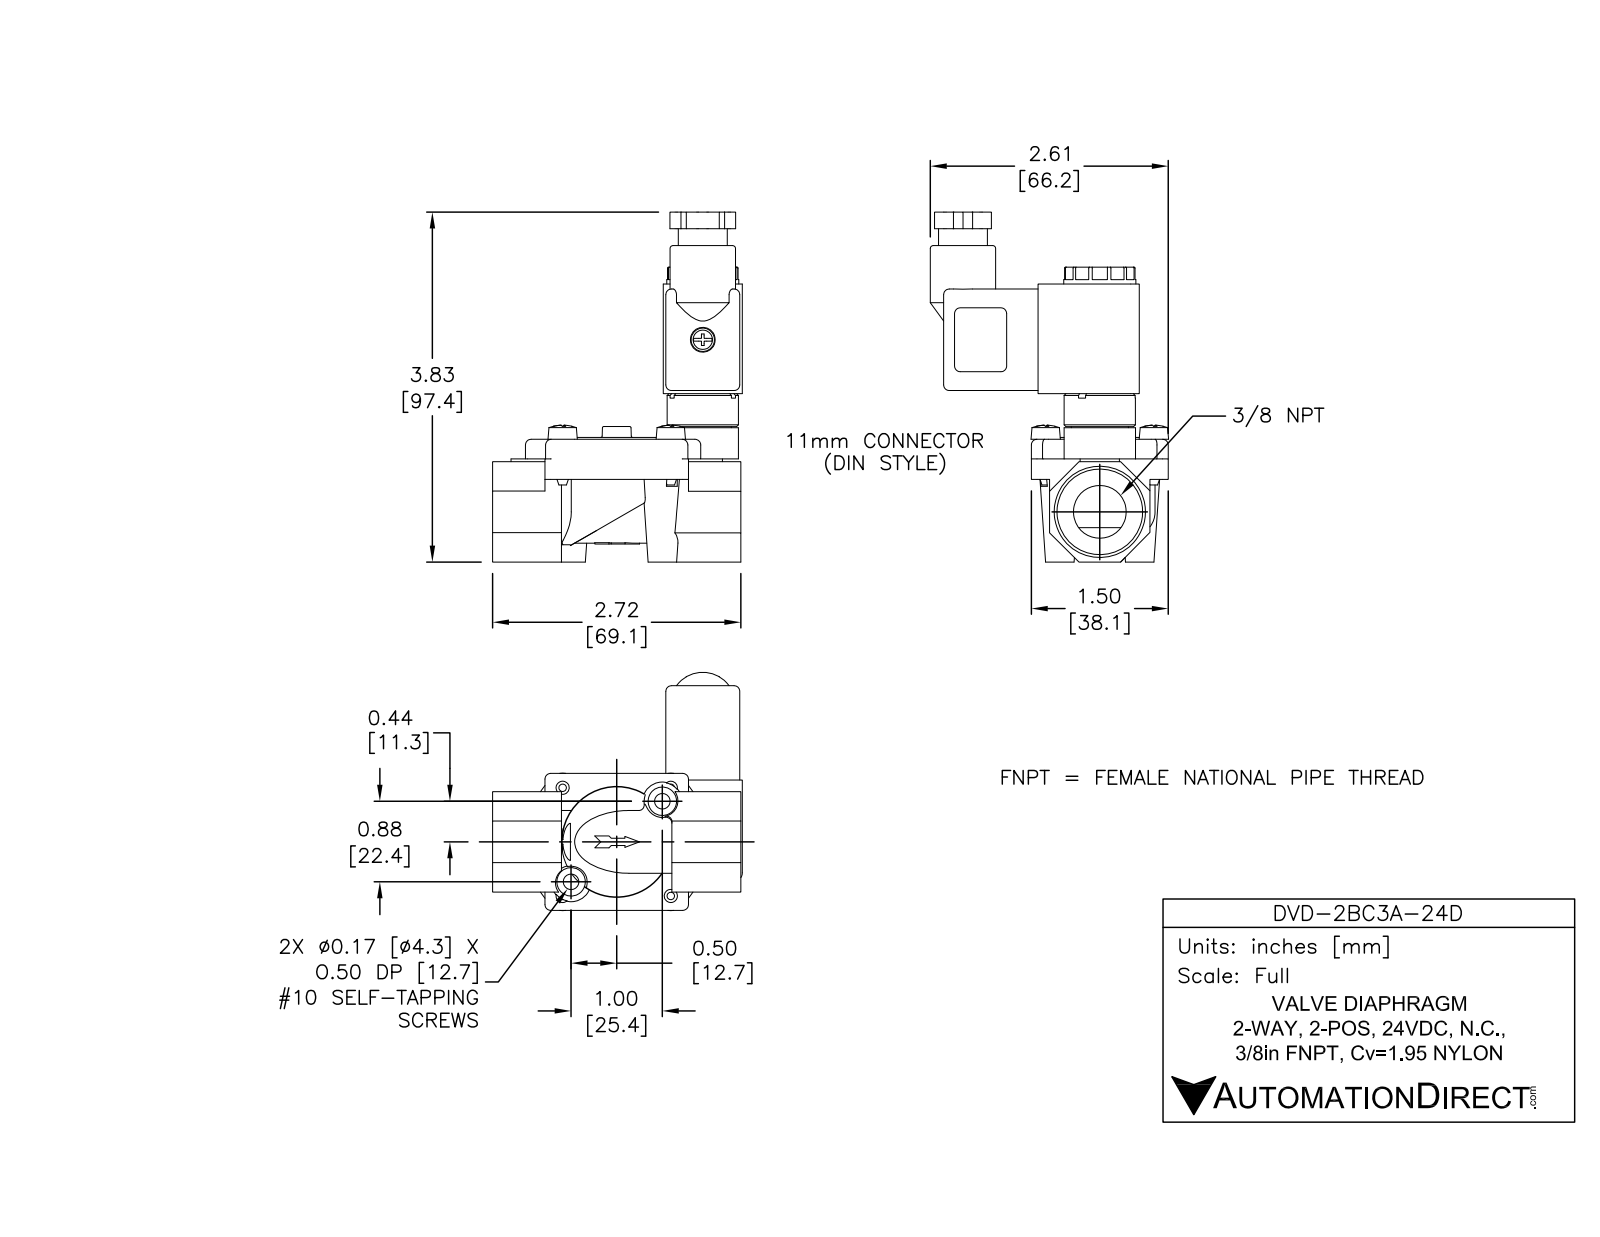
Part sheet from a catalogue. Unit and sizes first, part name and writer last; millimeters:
Units: millimetres
Overall size (bounding box): 97.4 × 69.5 × 66.3
Round holes (diameter × count): ⌀3.7 ×4, ⌀4.2 ×4, ⌀1.5 ×2, ⌀2.4 ×2, ⌀4.3 ×2, ⌀14.7 ×2, ⌀1.6 ×1, ⌀4 ×1, ⌀4.2 ×1, ⌀6.4 ×1, ⌀6.9 ×1, ⌀7.9 ×1
Round bosses / shafts (diameter × count): ⌀4.7 ×4, ⌀3.2 ×4, ⌀15.9 ×2, ⌀34.9 ×1, ⌀20.1 ×1, ⌀19.9 ×1, ⌀19.8 ×1, ⌀18.2 ×1
Partial cylindrical surfaces — rounded edges, fillets, slot ends (radius × count): R0.3 ×24, R1.6 ×24, R4 ×12, R1.1 ×3, R2.4 ×2, R5.5 ×2, R7.7 ×1, R8.7 ×1
Main face-to-face distances: 1.3, 27.9, 22, 19.3, 5.1, 33, 20, 2, 2, 18
Hole centre spacings: 21.3, 30.1, 4.6, 16.9, 17.5, 26.3, 28, 38.2
Volume: 65 810 mm³ · Surface area: 40 110 mm²
Bodies: 13 solids, 1441 faces (721 planar, 253 cylindrical, 467 other)
Part name (STEP PRODUCT): DVD-2BC3A-24D
STEP written by: SolidWorks 2015 (AUTOMOTIVE_DESIGN)
